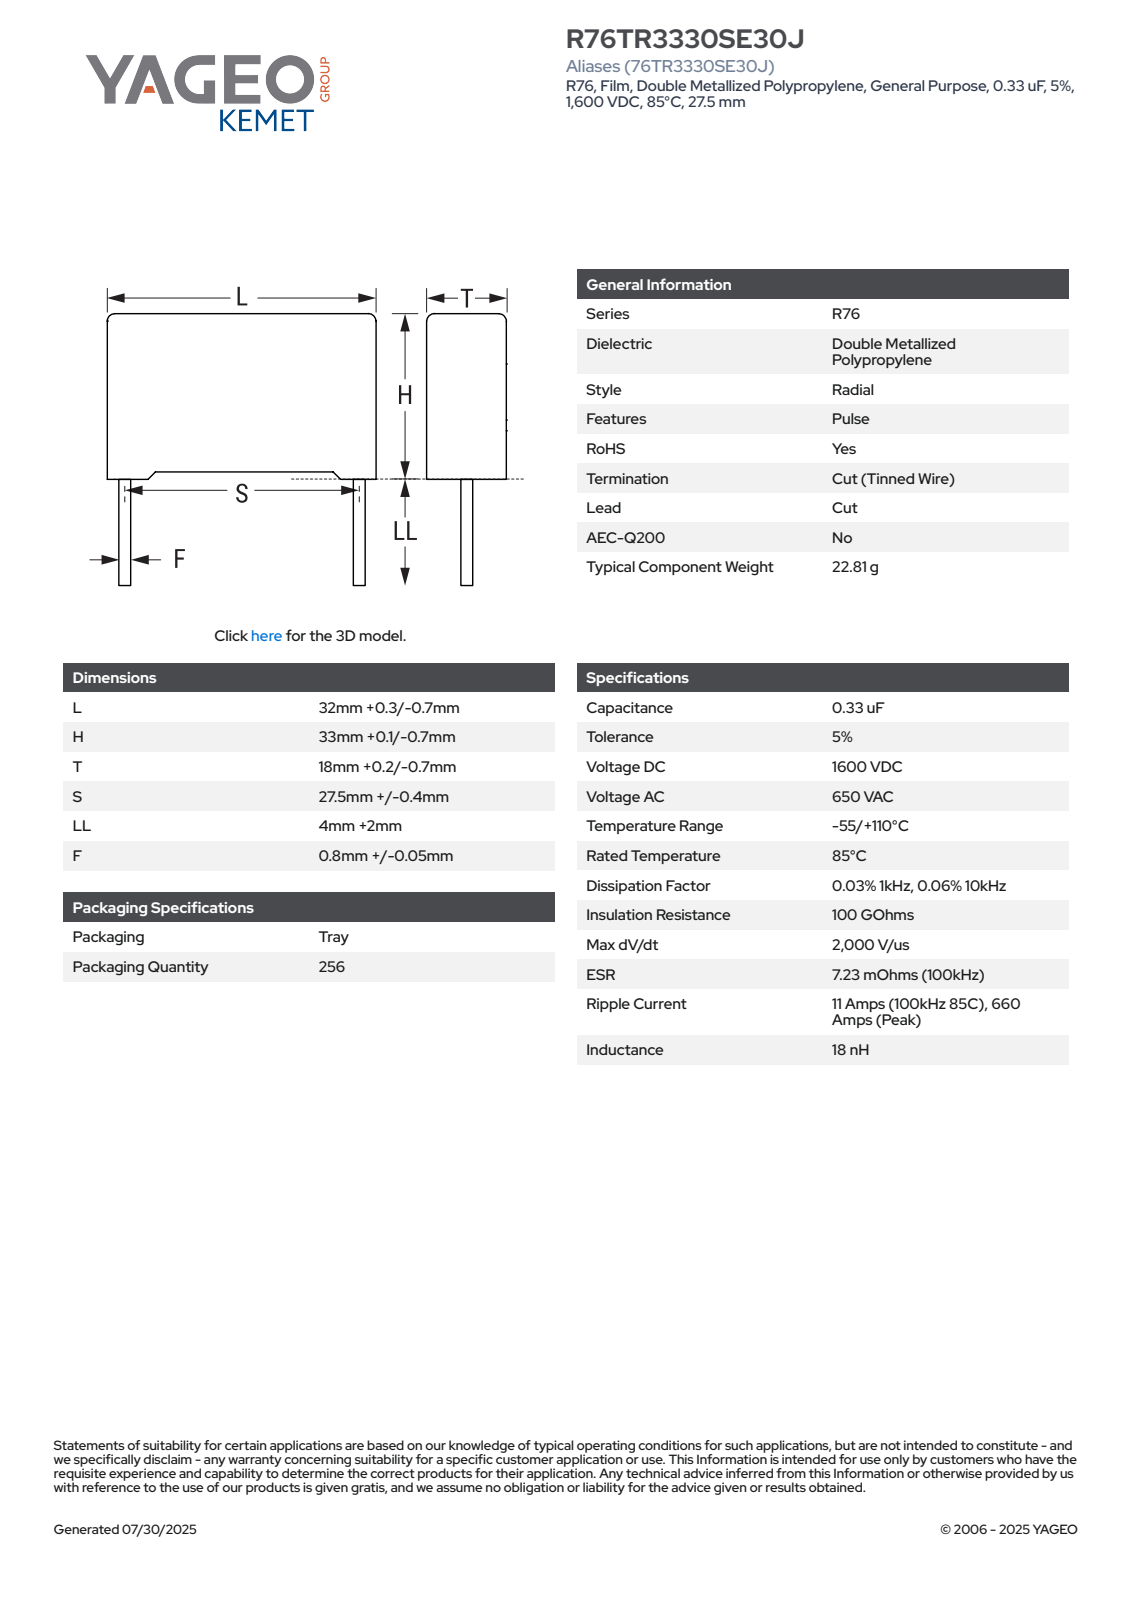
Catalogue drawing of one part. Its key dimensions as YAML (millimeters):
part_name: "CFR_RB2_32X33X18_L32.3H33.1T18.2S27.5LL6F0.85"
step_written_by: "SolidWorks 2021 (AUTOMOTIVE_DESIGN)"
units: millimeters
bodies: {solids: 4, faces: 85, planar: 77, cylindrical: 8, other: 0}
overall_size: [39.1, 32.3, 18.2]
volume: 18895
surface_area: 4599
round_bosses_or_shafts:
  - {diameter: 0.85, count: 2}
partial_cylinders:
  - {radius: 0.5, count: 4}
face_to_face_distances: [18.2, 32.3, 31.96, 0.39, 32.35, 0.75, 1.14, 33.1, 1.08, 31.22]
